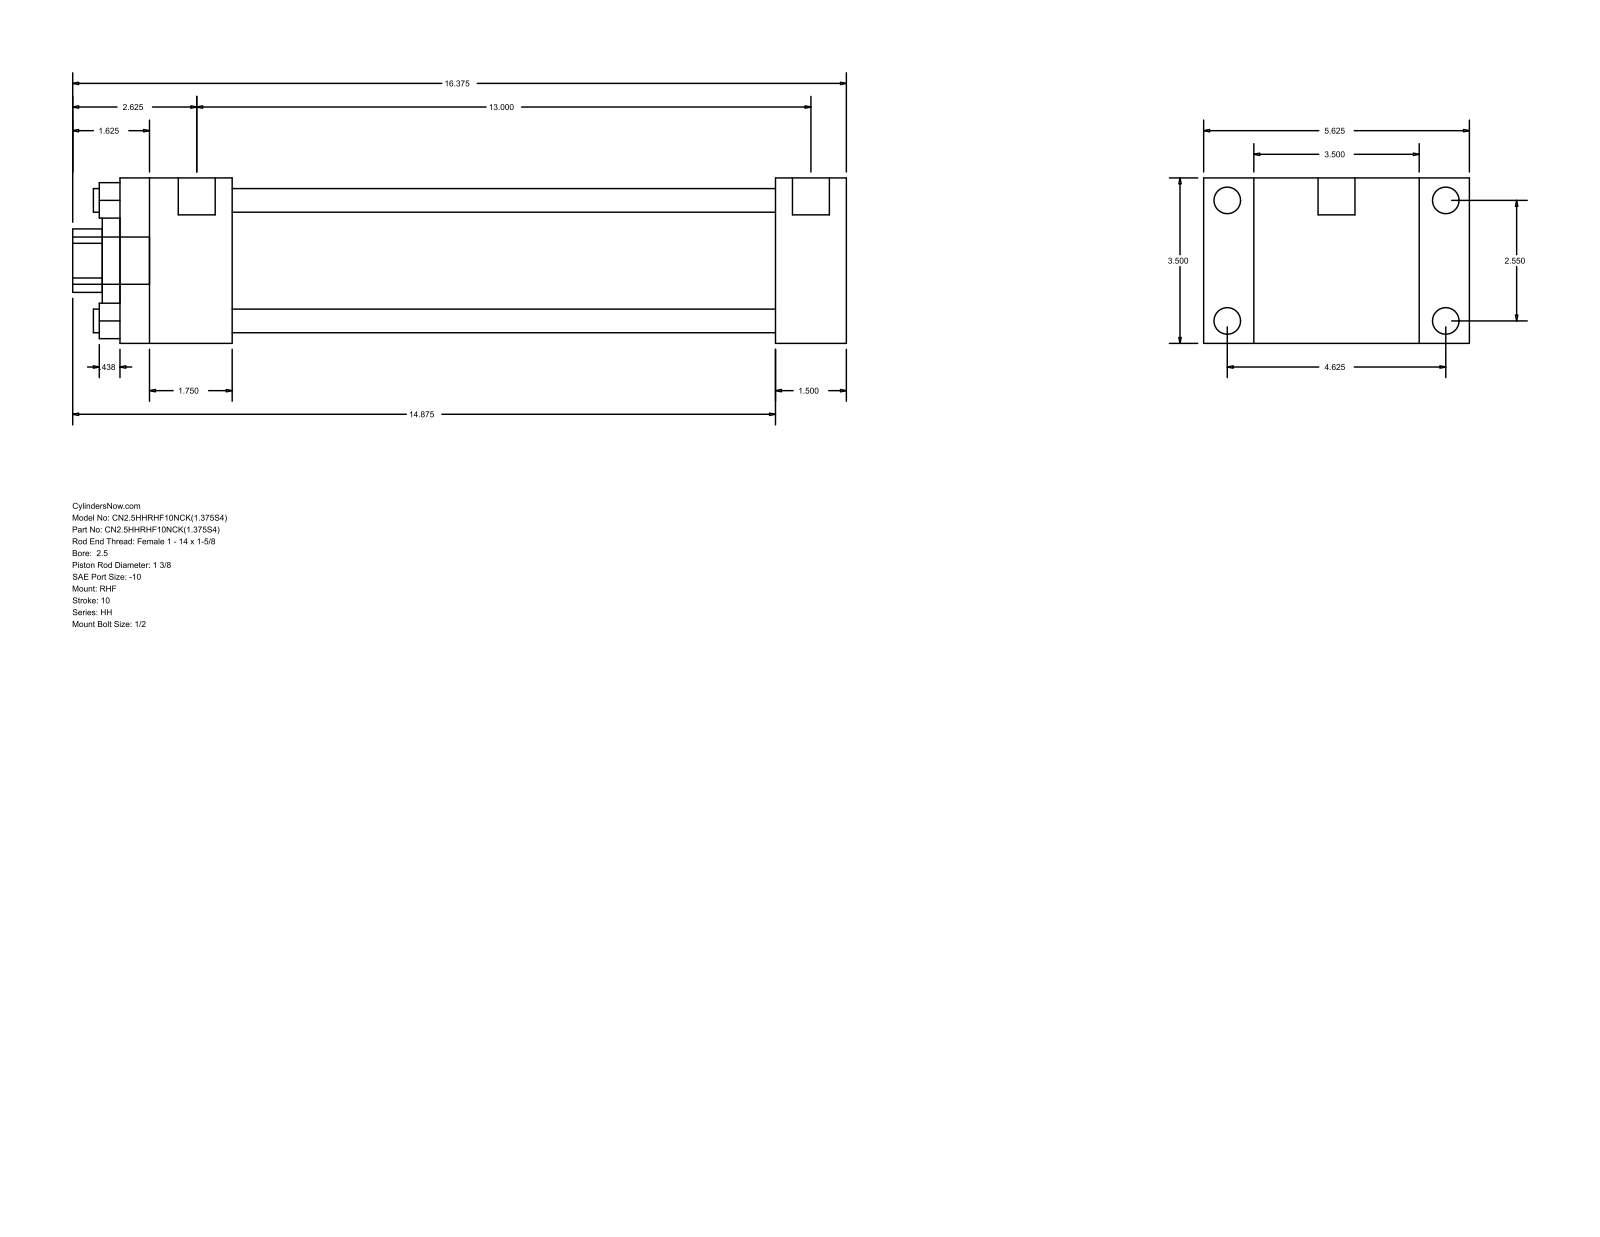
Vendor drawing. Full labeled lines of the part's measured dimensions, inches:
Part name (STEP PRODUCT): HH_RHF__0250_1.375
STEP written by: GSSL Pune (CONFIG_CONTROL_DESIGN)
Units: inches
Bodies: 0 solids, 88 faces (60 planar, 28 cylindrical, 0 other)
Overall size (bounding box): 16.375 × 5.625 × 3.5
Round holes (diameter × count): ⌀0.5 ×4, ⌀1.375 ×1, ⌀2 ×1, ⌀2.875 ×1
Round bosses / shafts (diameter × count): ⌀0.563 ×4, ⌀0.219 ×4, ⌀0.781 ×2, ⌀1 ×1
Partial cylindrical surfaces — rounded edges, fillets, slot ends (radius × count): R0.672 ×1
Main face-to-face distances: 3.5, 1.5, 1.063, 4.563, 13.875, 15.375, 5.625, 2.375, 11.5, 13
Hole centre spacings: 1.803, 2.55, 3.606
